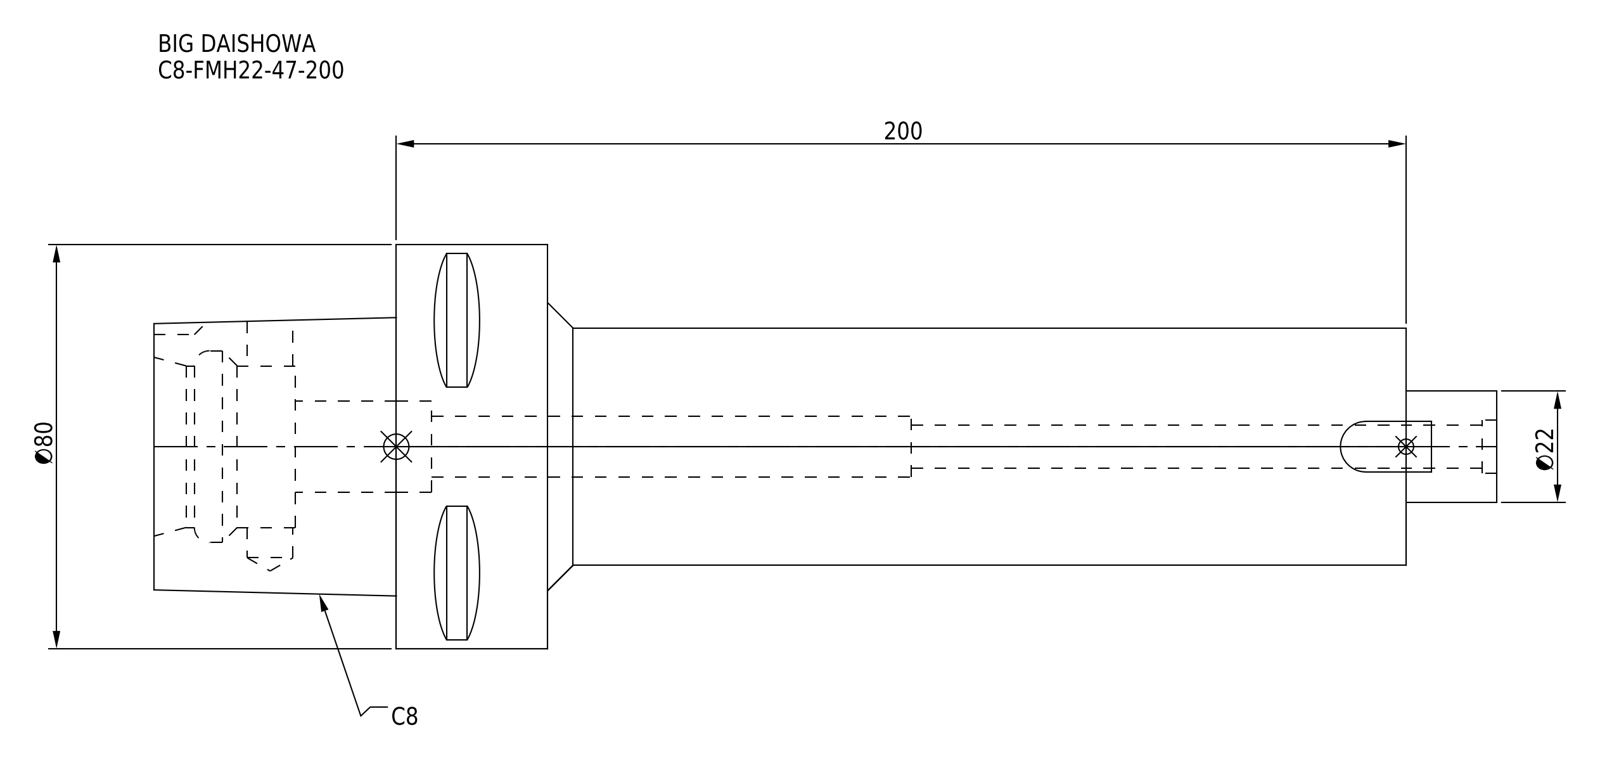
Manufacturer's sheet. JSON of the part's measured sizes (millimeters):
{"part_name": "C8-FMH22-47-200", "step_written_by": "CREO PARAMETRIC BY PTC INC, 2016380 (AUTOMOTIVE_DESIGN)", "units": "millimeters", "bodies": {"solids": 1, "faces": 78, "planar": 41, "cylindrical": 25, "other": 12}, "overall_size": [266, 80, 80], "volume_mm3": 510476, "surface_area_mm2": 63961, "round_holes": [[8.5, 1], [9.1, 1], [10.5, 1], [12, 1], [18, 1], [32, 1], [38, 1]], "round_bosses_or_shafts": [[80, 1], [47, 1], [22, 1]], "partial_cylinders_radius": [[6, 1]], "face_to_face_distances": [30, 170, 200, 248, 78, 48, 20, 220, 50, 28]}
